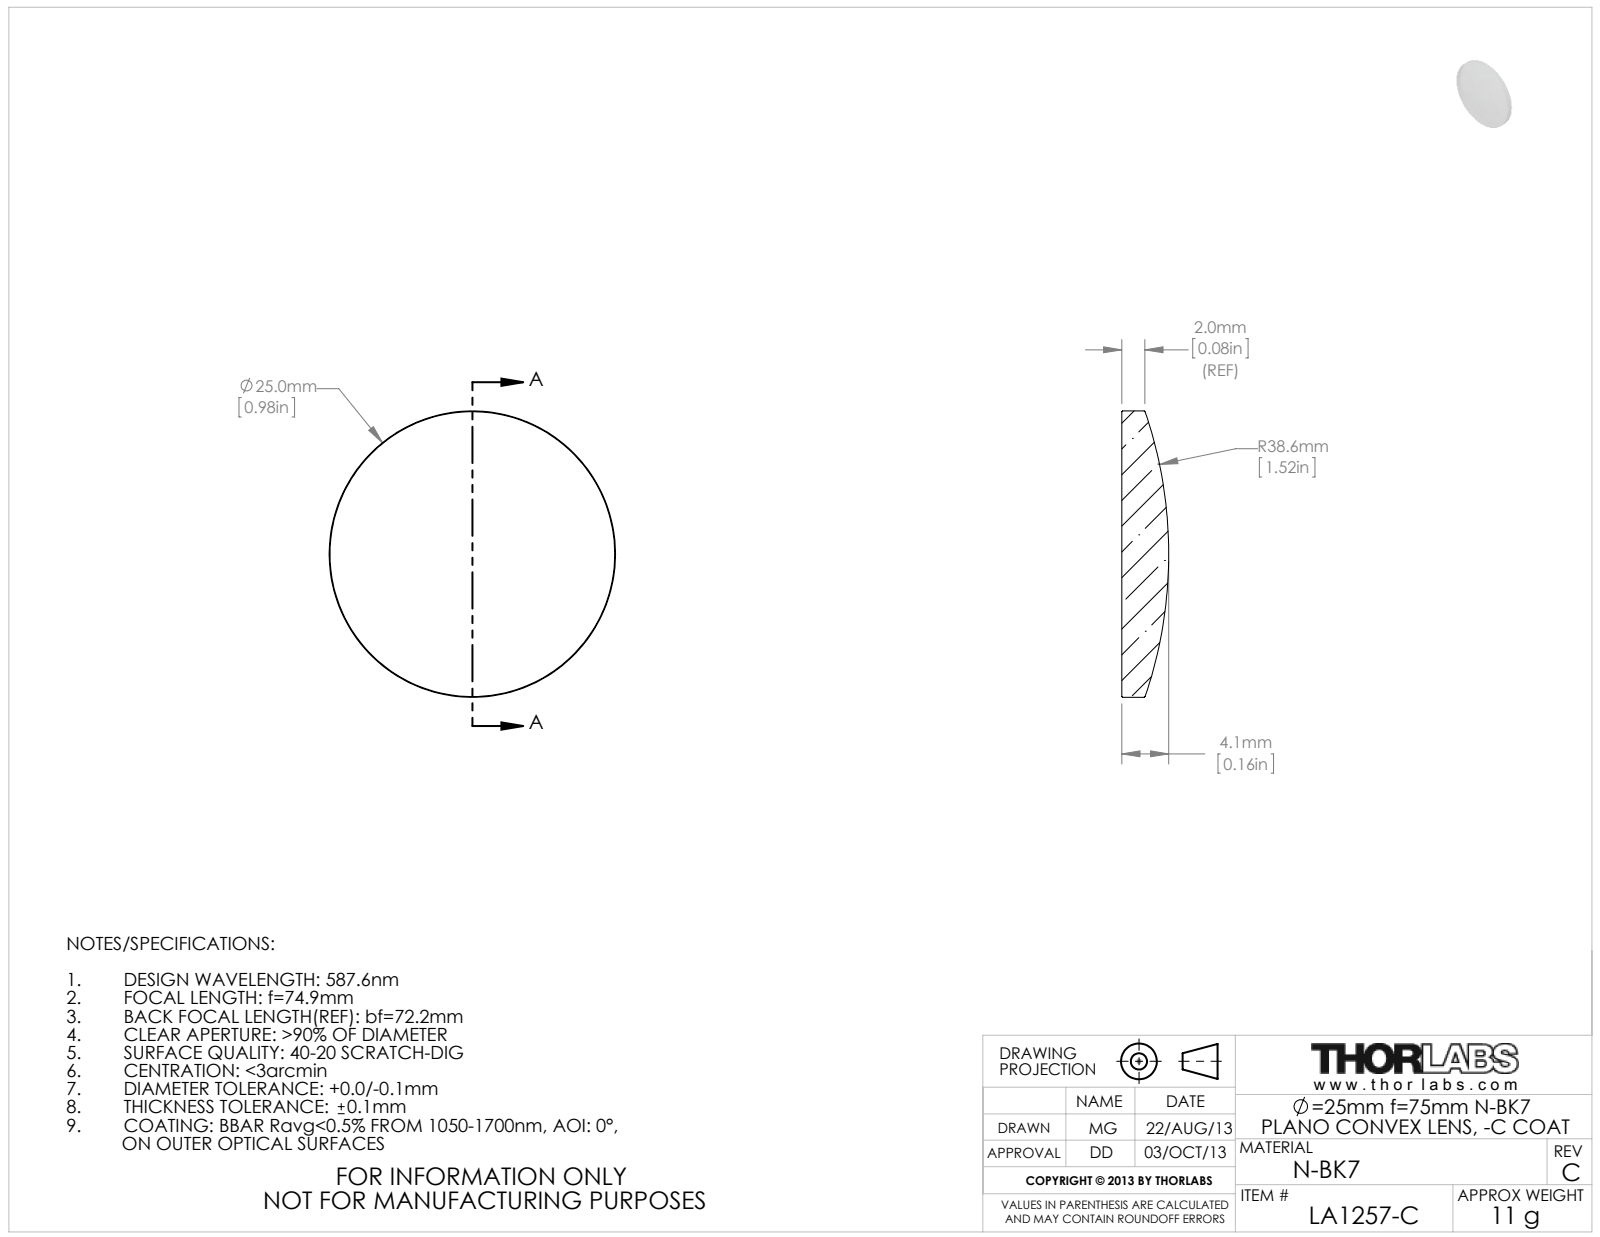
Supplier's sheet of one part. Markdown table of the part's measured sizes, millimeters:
| quantity | value |
| --- | --- |
| part name | 19054-E0W |
| STEP written by | SolidWorks 2009 (AUTOMOTIVE_DESIGN) |
| units | millimeters |
| bodies | 1 solid, 5 faces (1 planar, 2 cylindrical, 2 other) |
| overall size | 25 × 25 × 4.1 |
| volume | 1 507 mm³ |
| surface area | 1 154 mm² |
| round bosses / shafts (diameter × count) | 25 × 1 |
